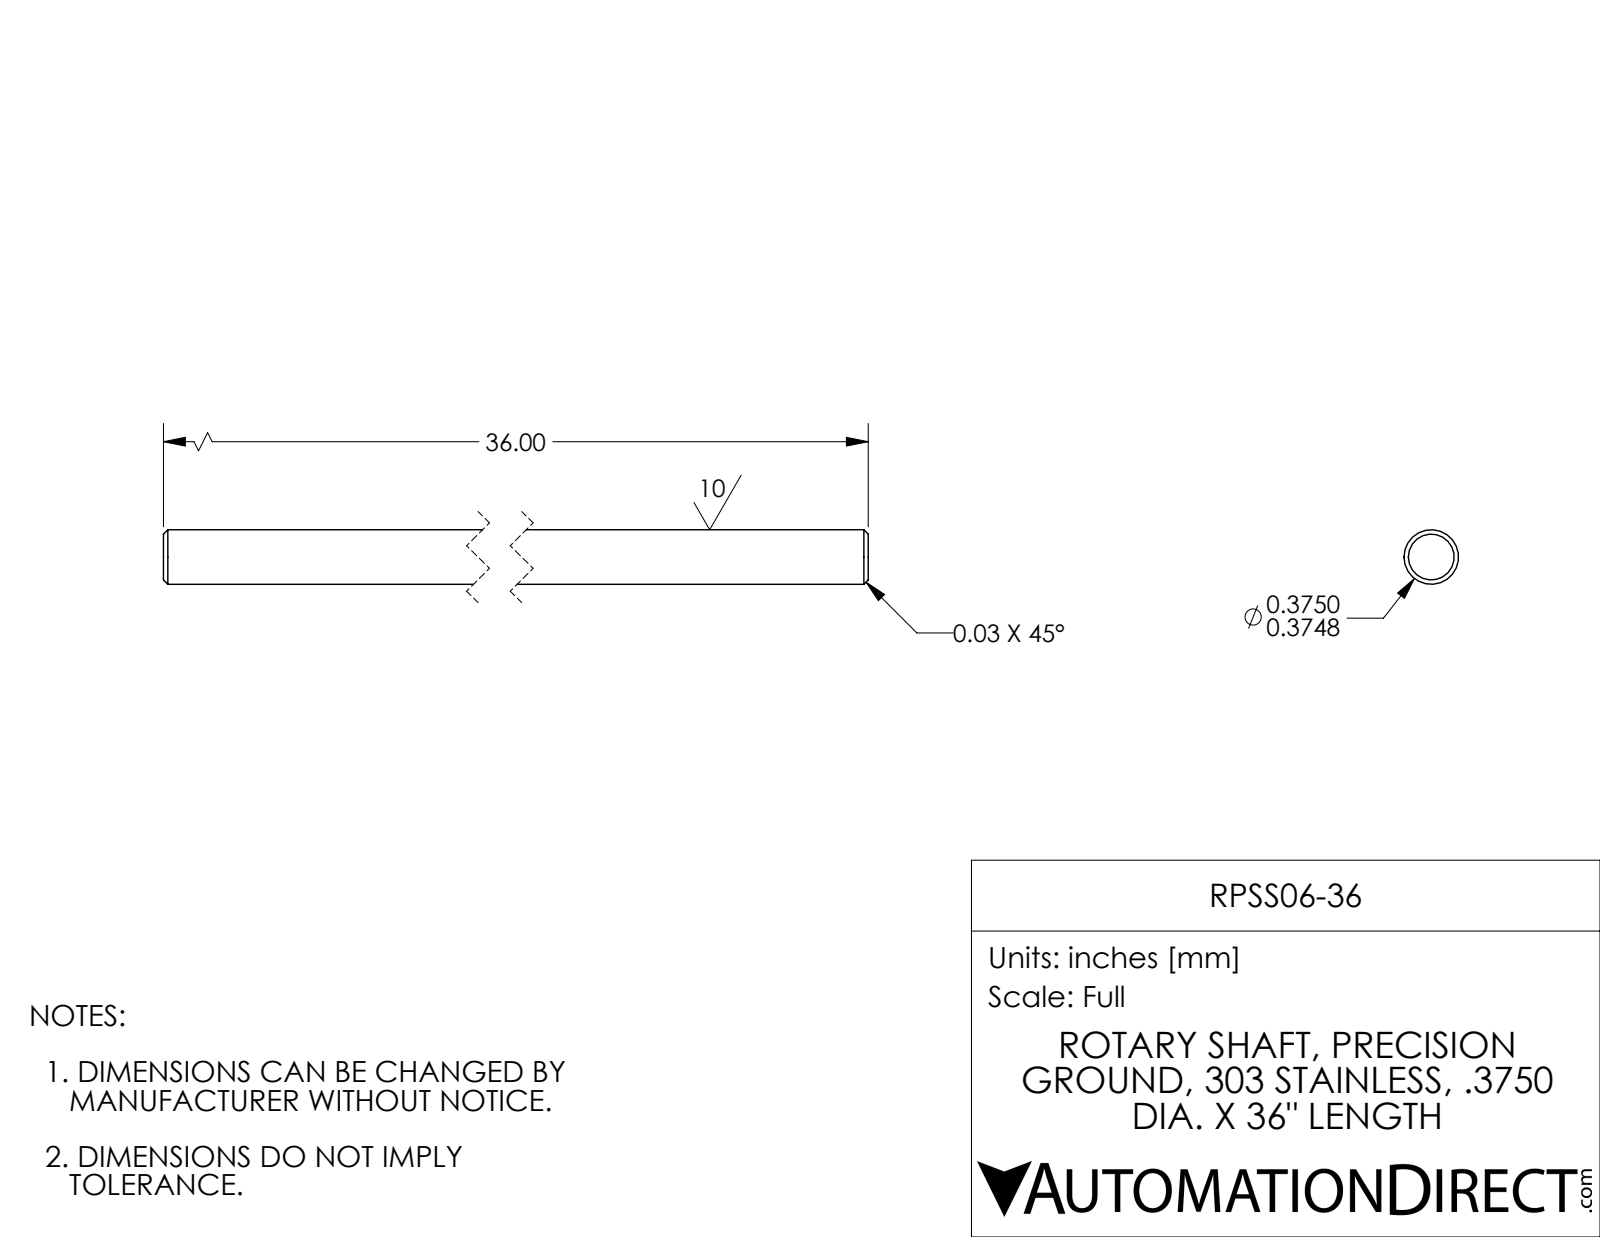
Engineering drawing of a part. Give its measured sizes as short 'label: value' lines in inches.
name: RPSS06-36
written by: SolidWorks 2017 (AUTOMOTIVE_DESIGN)
unit: in
bodies: 1 solid, 8 faces (2 planar, 2 cylindrical, 4 other)
size: 36 × 0.375 × 0.375
volume: 3.975 in³; area: 42.59 in²
bosses: 1× ⌀0.375
face distances: 36
